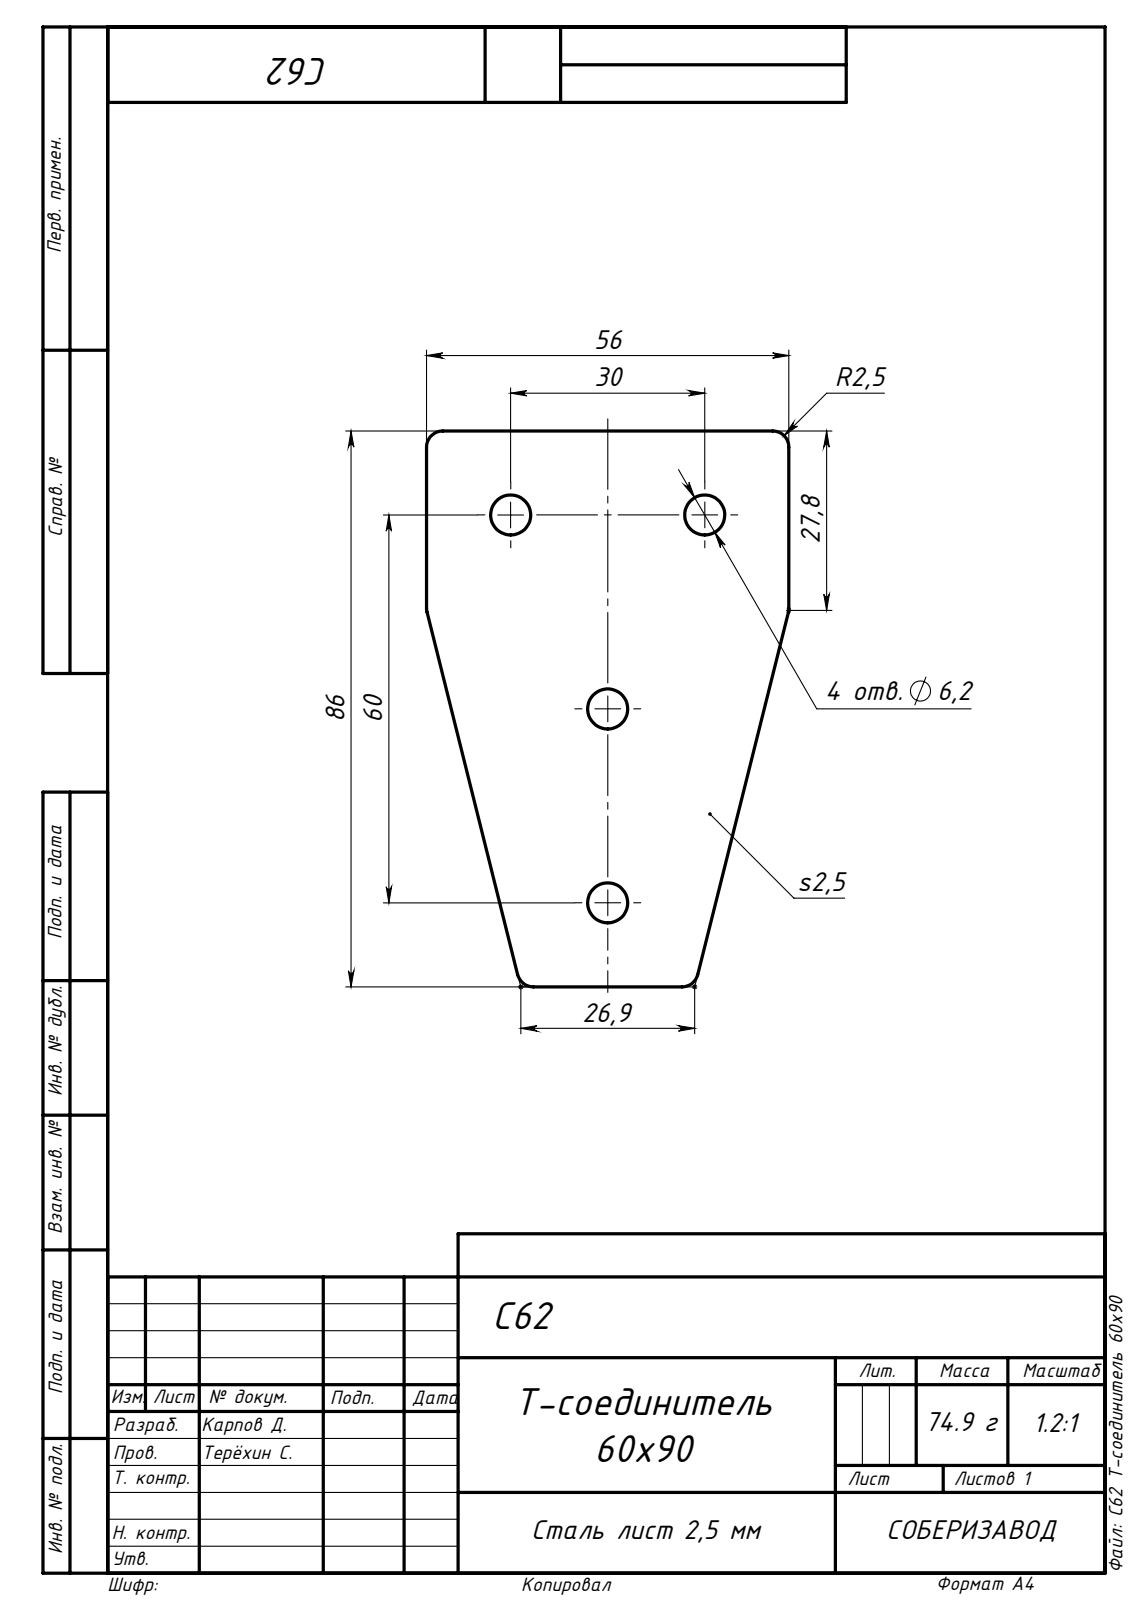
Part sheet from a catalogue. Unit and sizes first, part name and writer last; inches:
Units: inches
Overall size (bounding box): 3.386 × 2.205 × 0.098
Round holes (diameter × count): ⌀0.244 ×4
Partial cylindrical surfaces — rounded edges, fillets, slot ends (radius × count): R0.098 ×6
Main face-to-face distances: 0.098, 2.205, 3.386
Hole centre spacings: 1.181, 1.32, 2.435
Volume: 0.586 in³ · Surface area: 13.2 in²
Bodies: 1 solid, 22 faces (8 planar, 14 cylindrical, 0 other)
Part name (STEP PRODUCT): C62 Т-соединитель 60х90
STEP written by: SolidWorks 2019 (AUTOMOTIVE_DESIGN)
